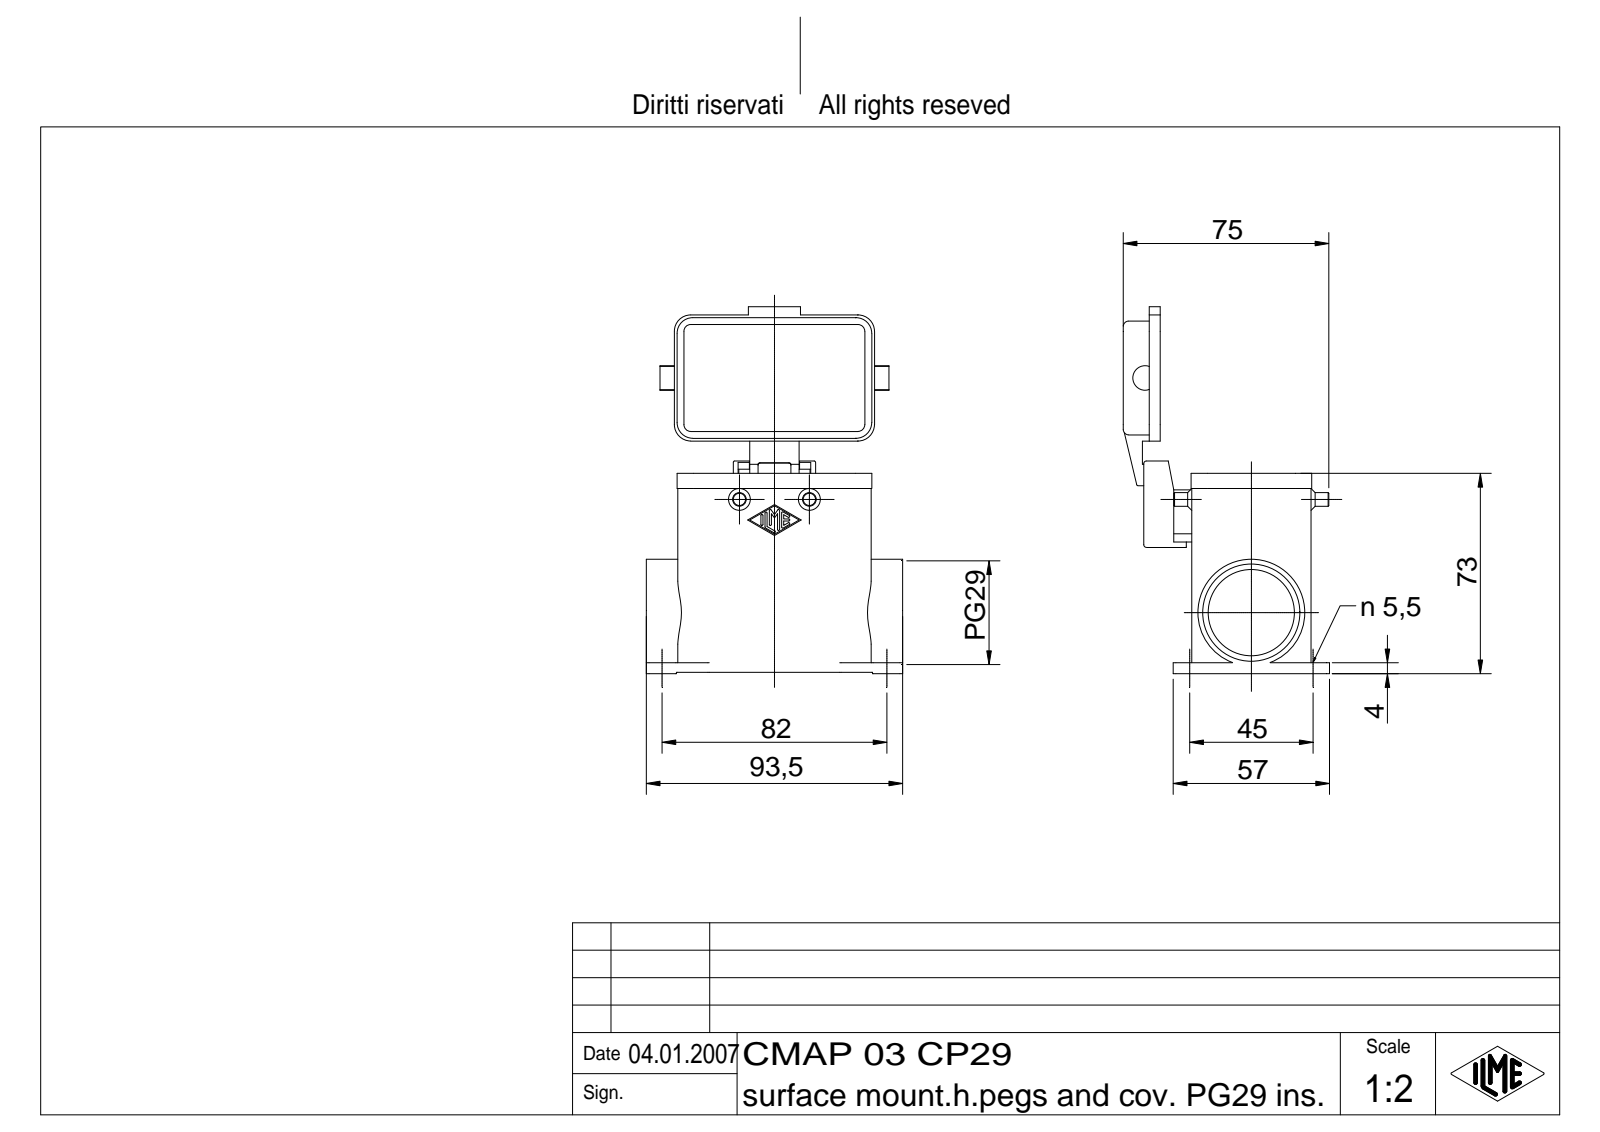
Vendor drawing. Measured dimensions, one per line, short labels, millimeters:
name: CMAP 03 CP29
written by: Autodesk Inventor 7 (AUTOMOTIVE_DESIGN)
unit: mm
bodies: 1 solid, 474 faces (197 planar, 166 cylindrical, 111 other)
size: 133.75 × 93.5 × 75.25
volume: 100 065 mm³; area: 62 179 mm²
holes: 4× ⌀5.5, 1× ⌀4, 1× ⌀5, 1× ⌀31.48, 1× ⌀35.48
bosses: 2× ⌀5, 2× ⌀3, 1× ⌀38.98, 1× ⌀7, 1× ⌀4
rounds: 14× R0.38, 14× R1, 12× R6, 10× R0.5, 8× R0.7, 8× R2, 4× R2.5, 4× R3
face distances: 3, 40.5, 43.5, 2.5, 68.5, 37.5, 66, 22.5, 3.5, 63
hole spacings: 45, 82, 93.54
